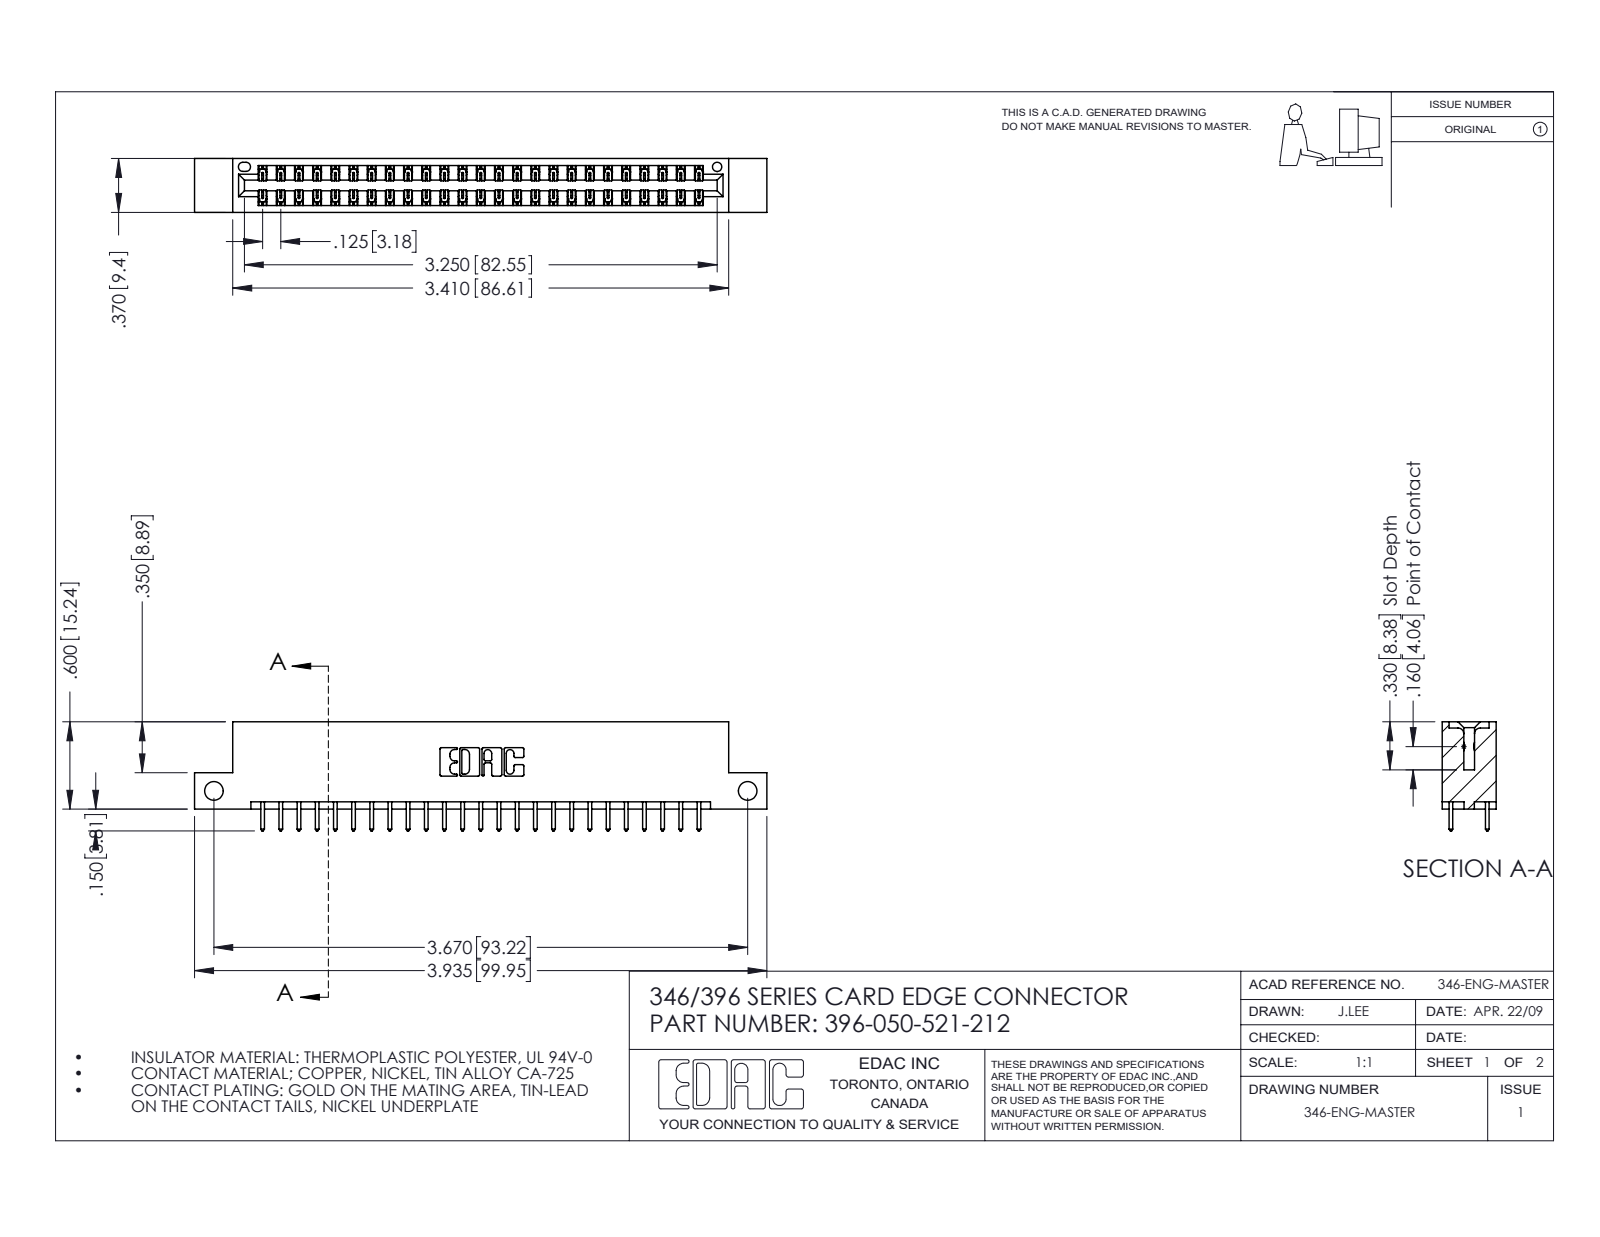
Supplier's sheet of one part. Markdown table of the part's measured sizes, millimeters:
| quantity | value |
| --- | --- |
| part name | 345-292-001_345-293-121; 346 Part_Flush Mounting Lugs - Side Mount; 396-050-521-212 |
| STEP written by | SolidWorks 2016 (CONFIG_CONTROL_DESIGN) |
| units | millimeters |
| bodies | 51 solids, 2722 faces (1826 planar, 896 cylindrical, 0 other) |
| overall size | 99.9 × 19.1 × 9.4 |
| volume | 9 500 mm³ |
| surface area | 12 520 mm² |
| round holes (diameter × count) | 3.3 × 2, 1.6 × 1 |
| partial cylindrical surfaces (radius × count) | 0.2 × 75, 0.3 × 50, 0.3 × 22, 0.2 × 6, 0.8 × 6, 0.7 × 3, 0.4 × 2, 0.6 × 2 |
| main face-to-face distances | 1.2, 8.2, 6.4, 9.4, 1.8, 7.6, 0.6, 7, 3.8, 5.6 |
| hole center spacings | 93.2 |
